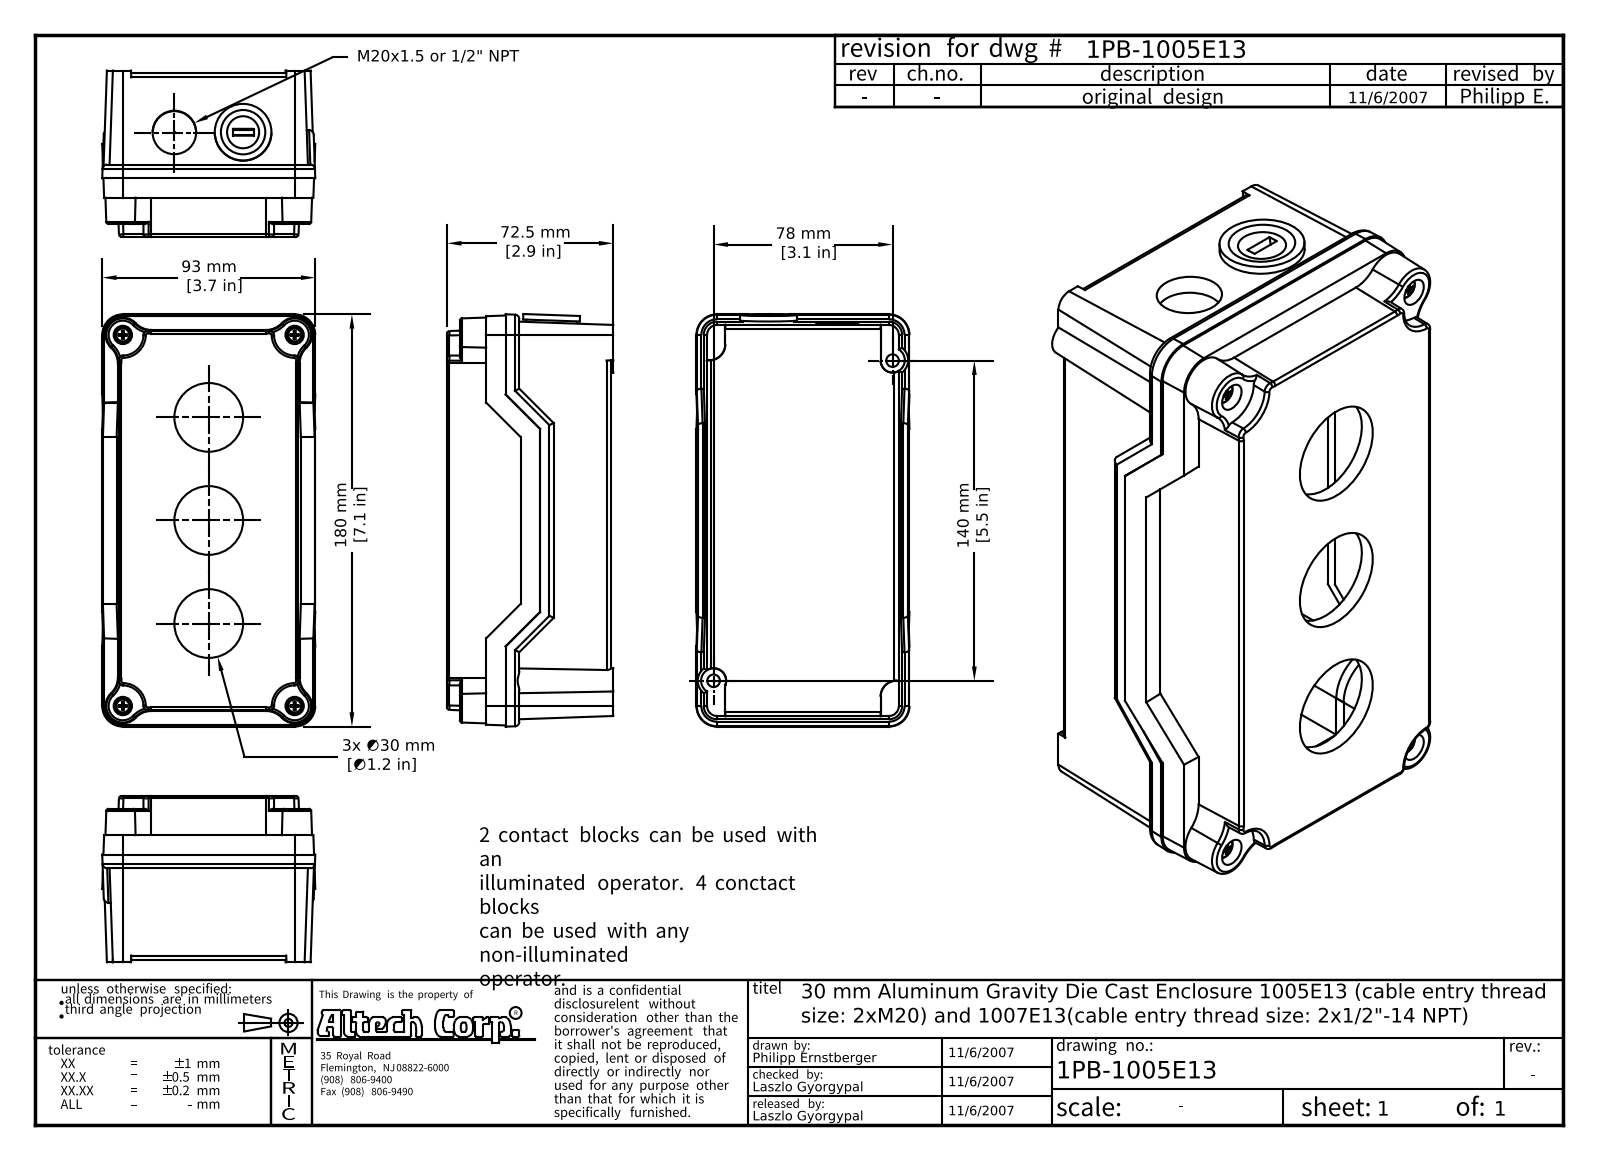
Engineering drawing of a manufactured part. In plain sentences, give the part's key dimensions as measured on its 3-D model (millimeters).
The part is named "1005E13; enclosure_back; enclosure_front; ISO 7045 Z M4 x 5 - 4.8 - Z (+4 more)". Its 3-D file was written by "Autodesk Inventor 2008 (AUTOMOTIVE_DESIGN)". It is 12 solids with 508 faces: 206 planar, 69 cylindrical and 233 other. Overall it measures 180.13 by 93 by 72.5 millimeters. Its volume is 349 909 cubic millimeters and its surface area 137 960 square millimeters. Round holes: 4 of diameter 3.5, 3 of diameter 30, 2 of diameter 4.3, 2 of diameter 19. Round bosses or shafts: 4 of diameter 3.18, 2 of diameter 9, 2 of diameter 4, 2 of diameter 3.62, 1 of diameter 24.75. Partial cylindrical surfaces (rounded edges, fillets, slot ends): 14 of radius 2, 6 of radius 9, 4 of radius 1, 3 of radius 12, 2 of radius 6, 2 of radius 8.5, 2 of radius 11.5, 1 of radius 7.75. The main face-to-face distances are 6, 65.5, 71.5, 67, 4.5, 61, 74, 40, 21, 46. The hole center spacings are 51.98, 89.26, 131.46, 30.51, 33.51, 45, 60.59, 75.
